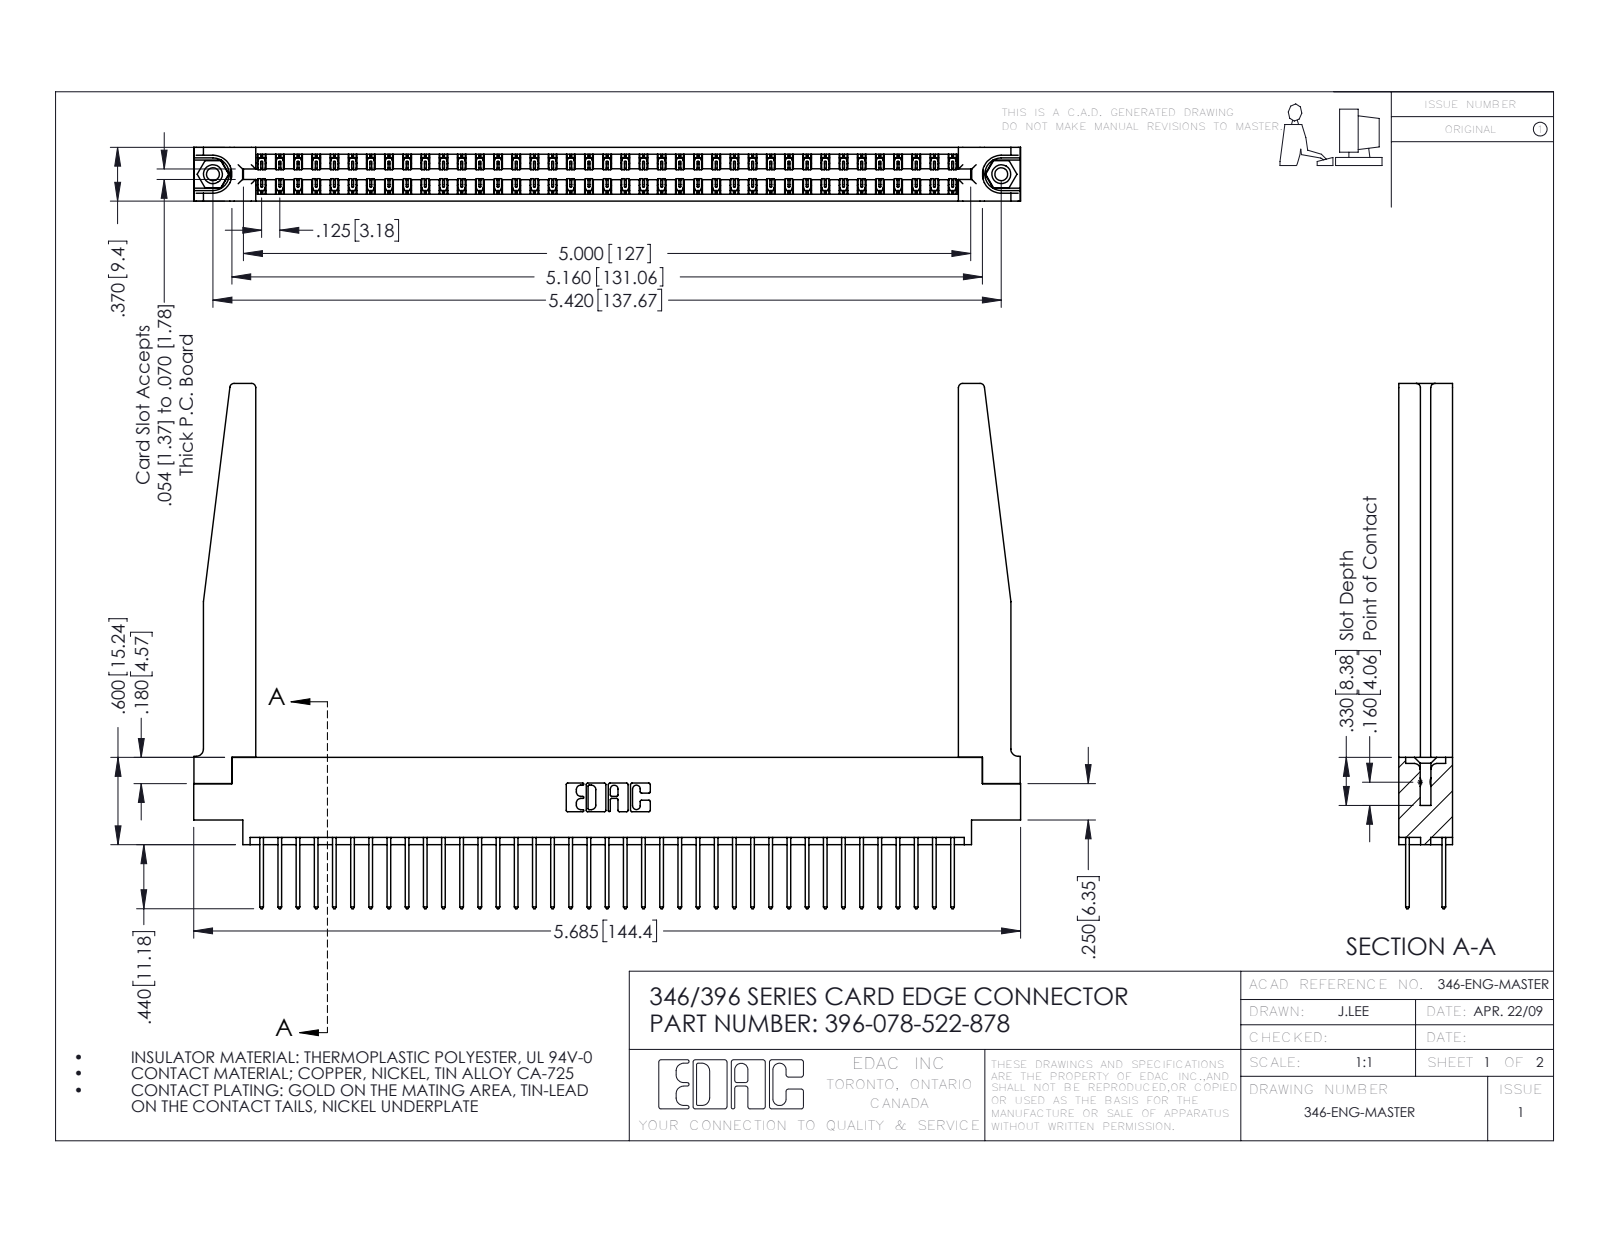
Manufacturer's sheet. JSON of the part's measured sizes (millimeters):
{"part_name": "346-220-078_345-220-078; 396-078-522-878; 345-250-001_345-250-001-102; 345-292-001_345-293-122 (+1 more)", "step_written_by": "SolidWorks 2016 (CONFIG_CONTROL_DESIGN)", "units": "millimeters", "bodies": {"solids": 83, "faces": 4416, "planar": 2952, "cylindrical": 1412, "other": 52}, "overall_size": [144.4, 91.7, 9.4], "volume_mm3": 21010, "surface_area_mm2": 26980, "round_holes": [[2.3, 2], [3.2, 2], [4, 2], [1.6, 1]], "round_bosses_or_shafts": [[3.9, 2]], "partial_cylinders_radius": [[0.2, 117], [0.3, 78], [0.3, 22], [0.8, 8], [0.2, 6], [0.8, 6], [0.7, 3], [0.4, 2]], "face_to_face_distances": [9.4, 1.2, 8.2, 1.8, 6.4, 7.6, 0.6, 3.8, 3.8, 7], "hole_center_spacings": [6.2, 132.4, 137.7]}
